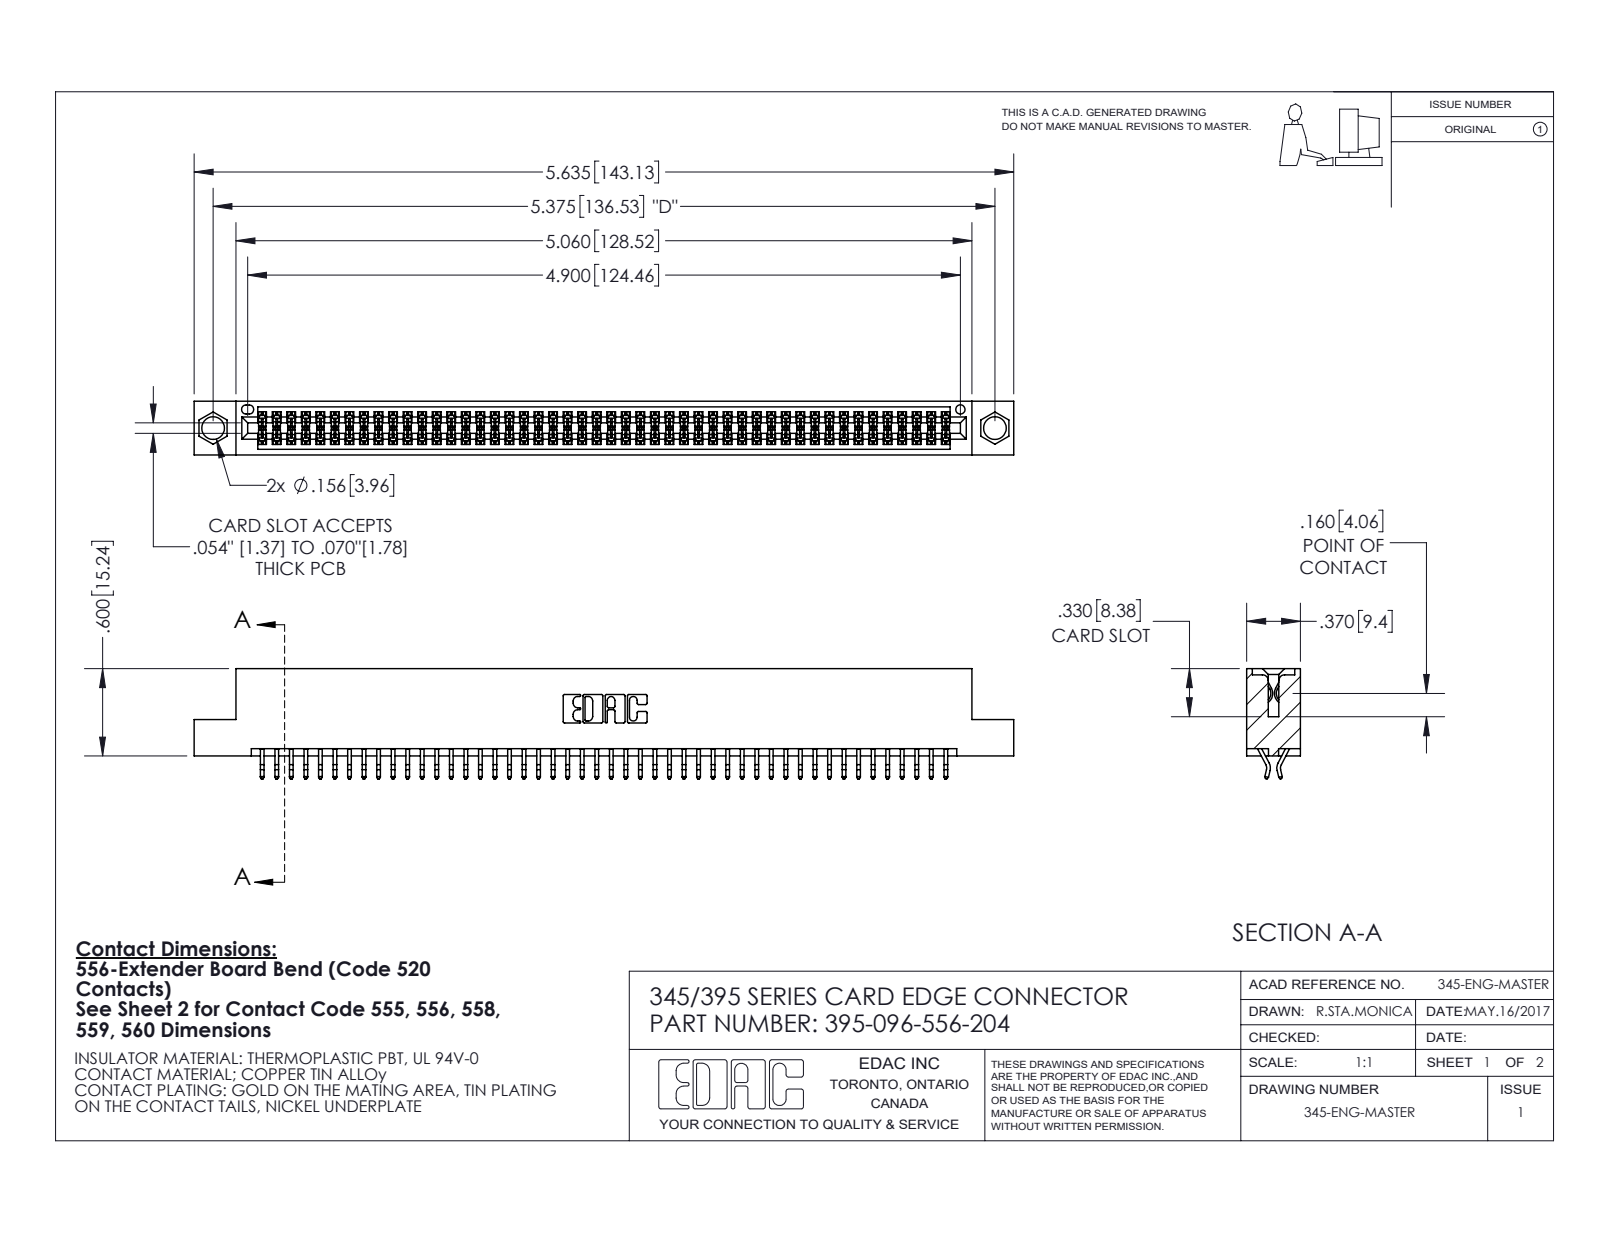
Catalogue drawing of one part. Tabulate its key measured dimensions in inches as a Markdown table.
| quantity | value |
| --- | --- |
| part name | 395-096-556-204; 345-292-001_556 Tail; 345 Part_Flush Mounting Lugs - 0.156 Dia-TI |
| STEP written by | SolidWorks 2020 (CONFIG_CONTROL_DESIGN) |
| units | inches |
| bodies | 97 solids, 5516 faces (3646 planar, 1870 cylindrical, 0 other) |
| overall size | 5.635 × 0.757 × 0.37 |
| volume | 0.845 in³ |
| surface area | 31.55 in² |
| round holes (diameter × count) | 0.156 × 2, 0.064 × 1 |
| partial cylindrical surfaces (radius × count) | 0.006 × 192, 0.01 × 22, 0.007 × 6, 0.031 × 6, 0.026 × 3, 0.01 × 2, 0.014 × 2, 0.019 × 2 |
| main face-to-face distances | 0.298, 0.072, 0.37, 0.2, 0.025, 0.098, 0.272, 0.225, 0.175, 0.149 |
| hole center spacings | 0.27, 5.139, 5.375 |
